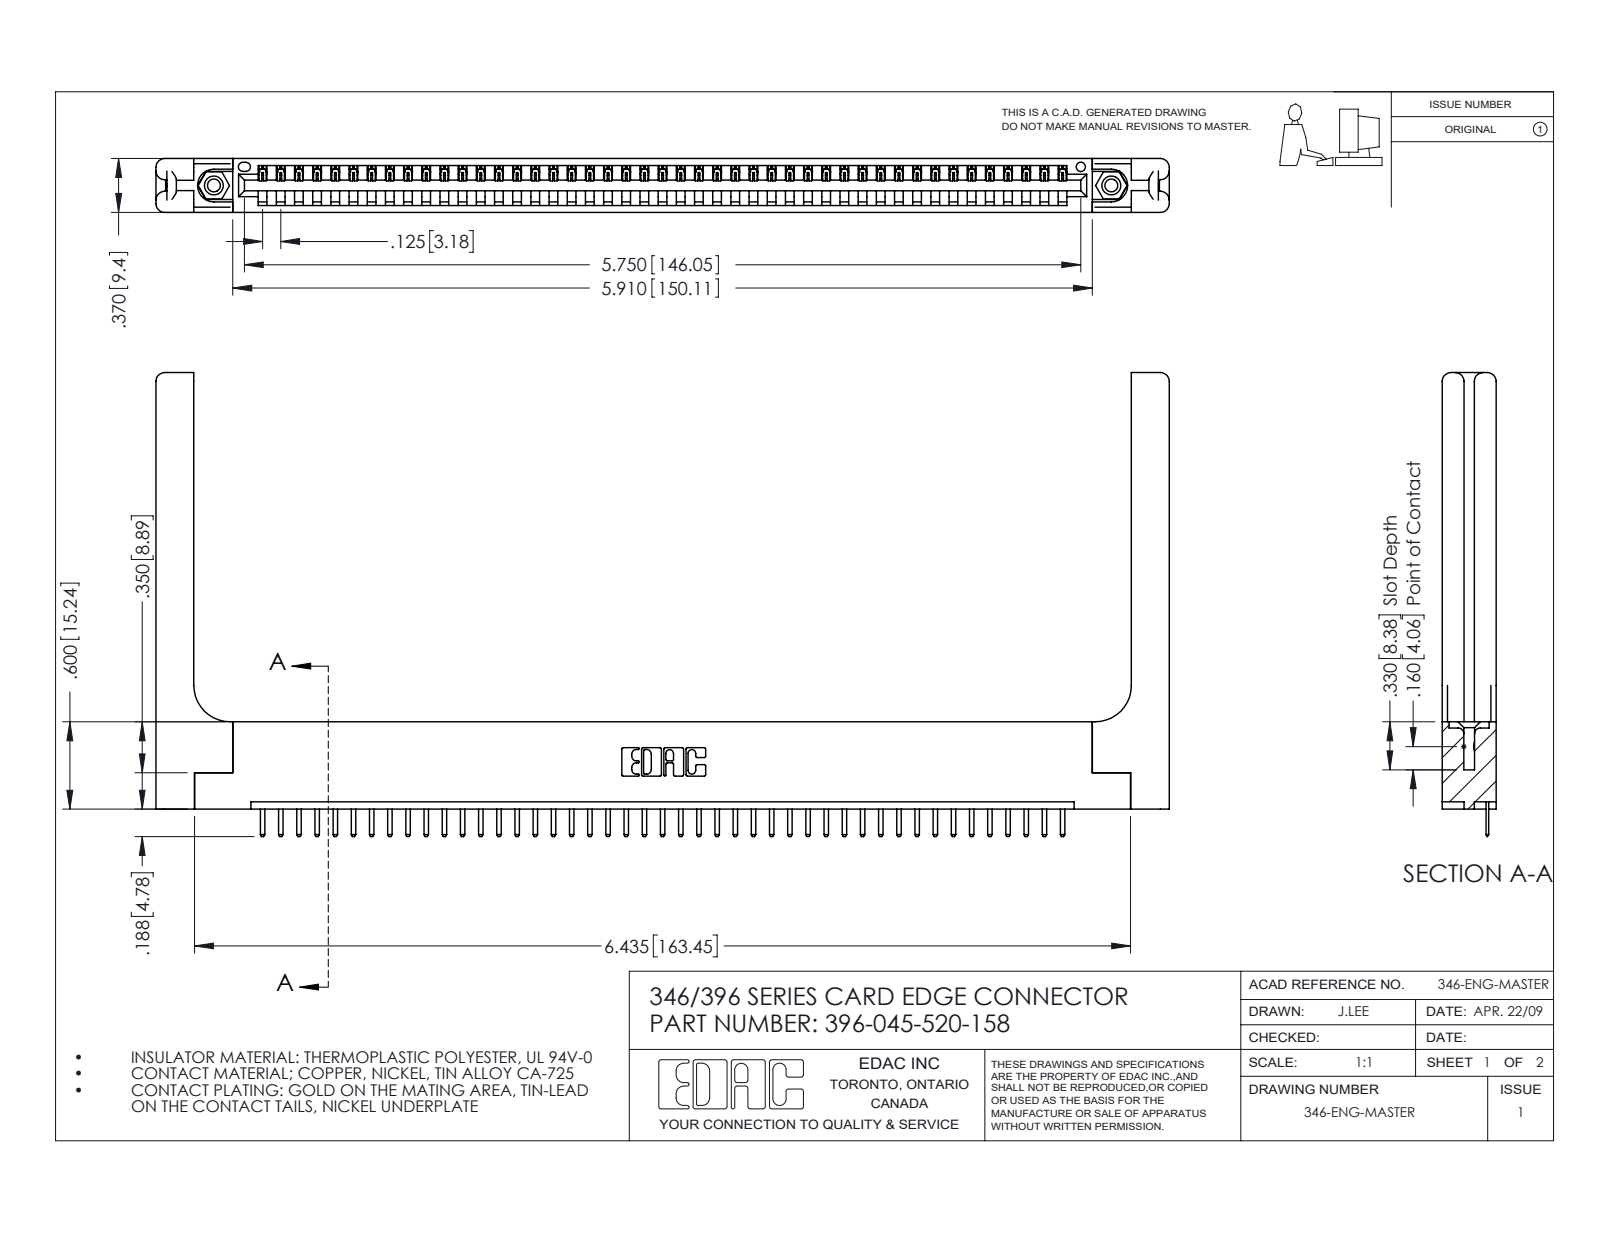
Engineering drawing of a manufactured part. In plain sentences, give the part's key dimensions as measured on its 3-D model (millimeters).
The part is named "346-220-058_345-220-058; 396-045-520-158; 346 Part_Flush Mounting Lugs - 0.156 Dia-TH; 345-292-001_345-293-120 (+1 more)". Its 3-D file was written by "SolidWorks 2016 (CONFIG_CONTROL_DESIGN)". It is 50 solids with 3168 faces: 2114 planar, 994 cylindrical and 60 other. Overall it measures 176.9 by 81 by 9.4 millimeters. Its volume is 24 350 cubic millimeters and its surface area 25 800 square millimeters. Round holes: 2 of diameter 2.3, 2 of diameter 3.2, 2 of diameter 4, 1 of diameter 1.6. Round bosses or shafts: 2 of diameter 3.9. Partial cylindrical surfaces (rounded edges, fillets, slot ends): 92 of radius 0.3, 90 of radius 0.2, 22 of radius 0.3, 16 of radius 1.5, 6 of radius 0.2, 6 of radius 0.8, 3 of radius 0.7, 2 of radius 0.8. The main face-to-face distances are 9.4, 1.2, 8.2, 1.8, 3.8, 3.8, 6.4, 7.6, 0.6, 5.6. The hole center spacings are 6.2, 151.4, 156.7.
